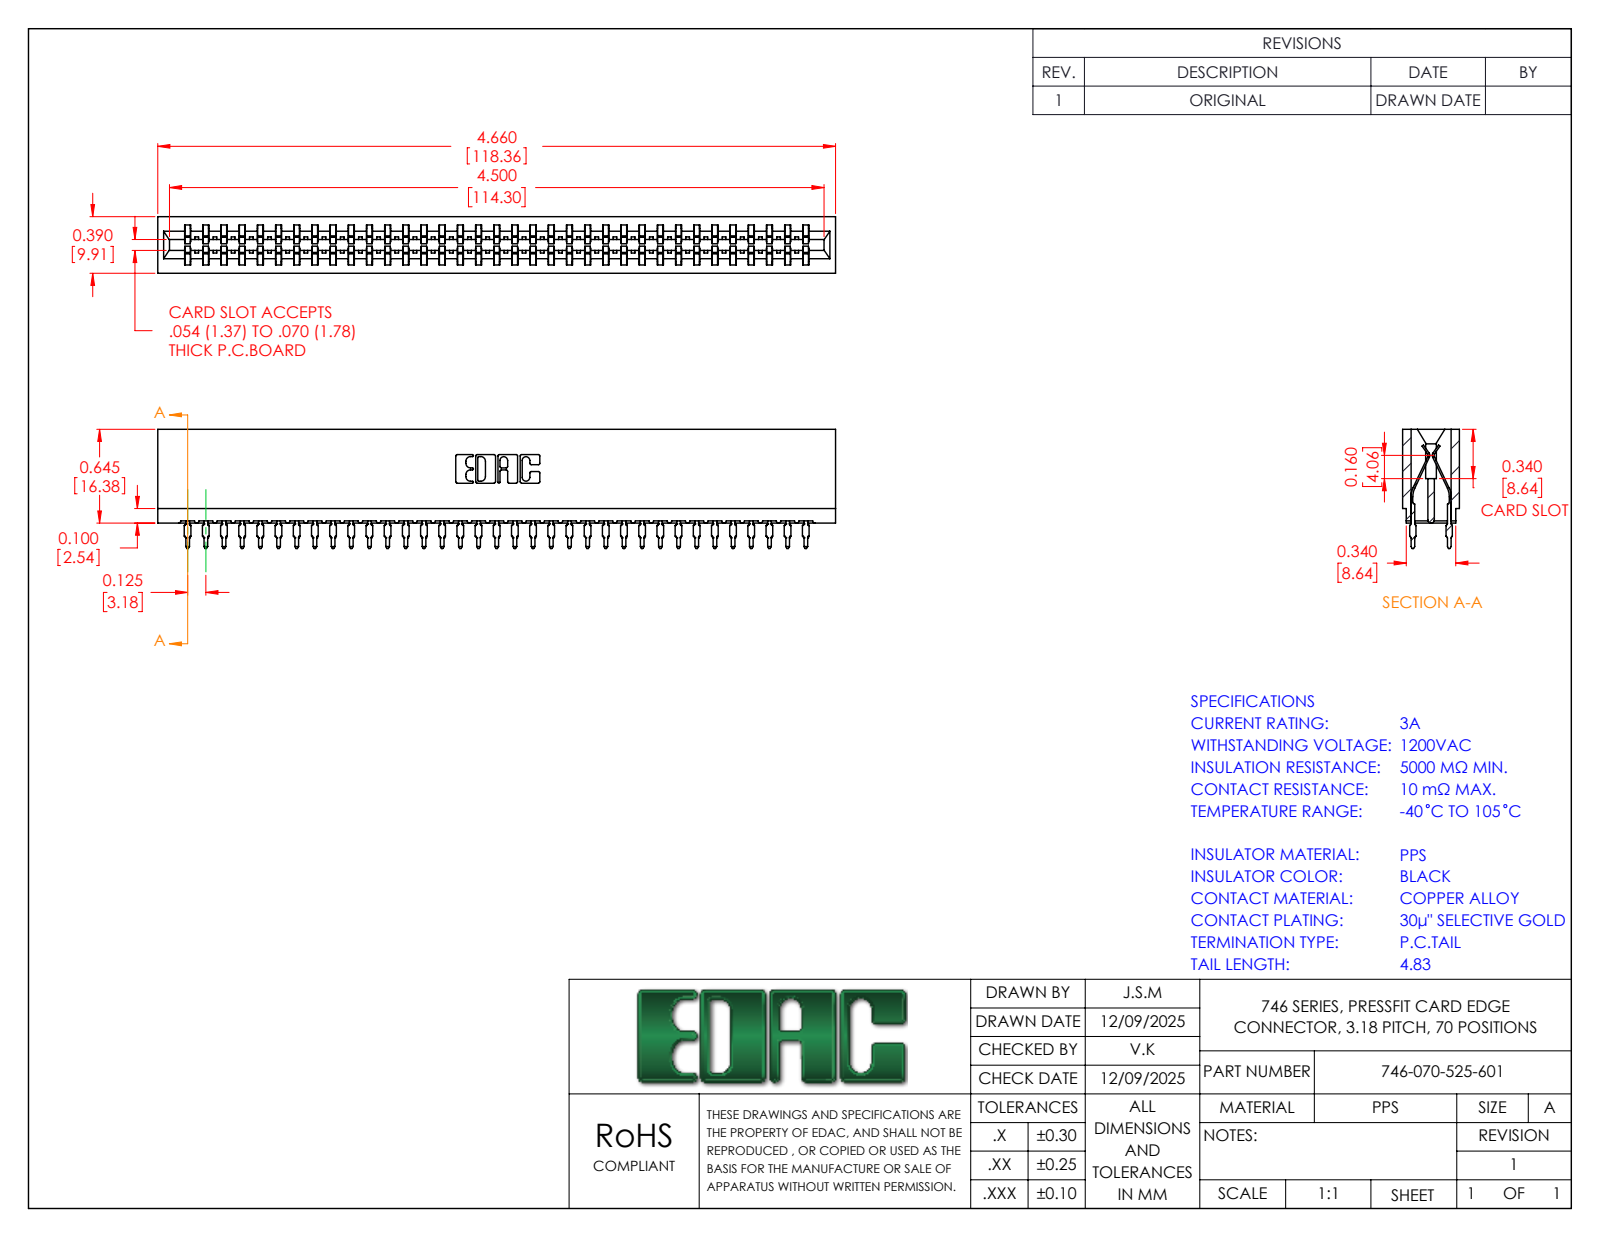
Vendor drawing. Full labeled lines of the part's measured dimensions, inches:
Part name (STEP PRODUCT): 746-292-001_525; 746-070-525-601; 746 Part_.340 Slot Depth - 01
STEP written by: SolidWorks 2023 (CONFIG_CONTROL_DESIGN)
Units: inches
Bodies: 71 solids, 6362 faces (3275 planar, 1267 cylindrical, 1820 other)
Overall size (bounding box): 4.66 × 0.82 × 0.39
Volume: 0.831 in³ · Surface area: 30.45 in²
Partial cylindrical surfaces — rounded edges, fillets, slot ends (radius × count): R0.022 ×140, R0.015 ×36, R0.01 ×22, R0.005 ×8, R0.011 ×8, R0.007 ×6, R0.031 ×6, R0.026 ×3
Main face-to-face distances: 0.057, 0.333, 0.39, 0.25, 0.025, 0.307, 0.275, 0.083, 0.5, 0.015
